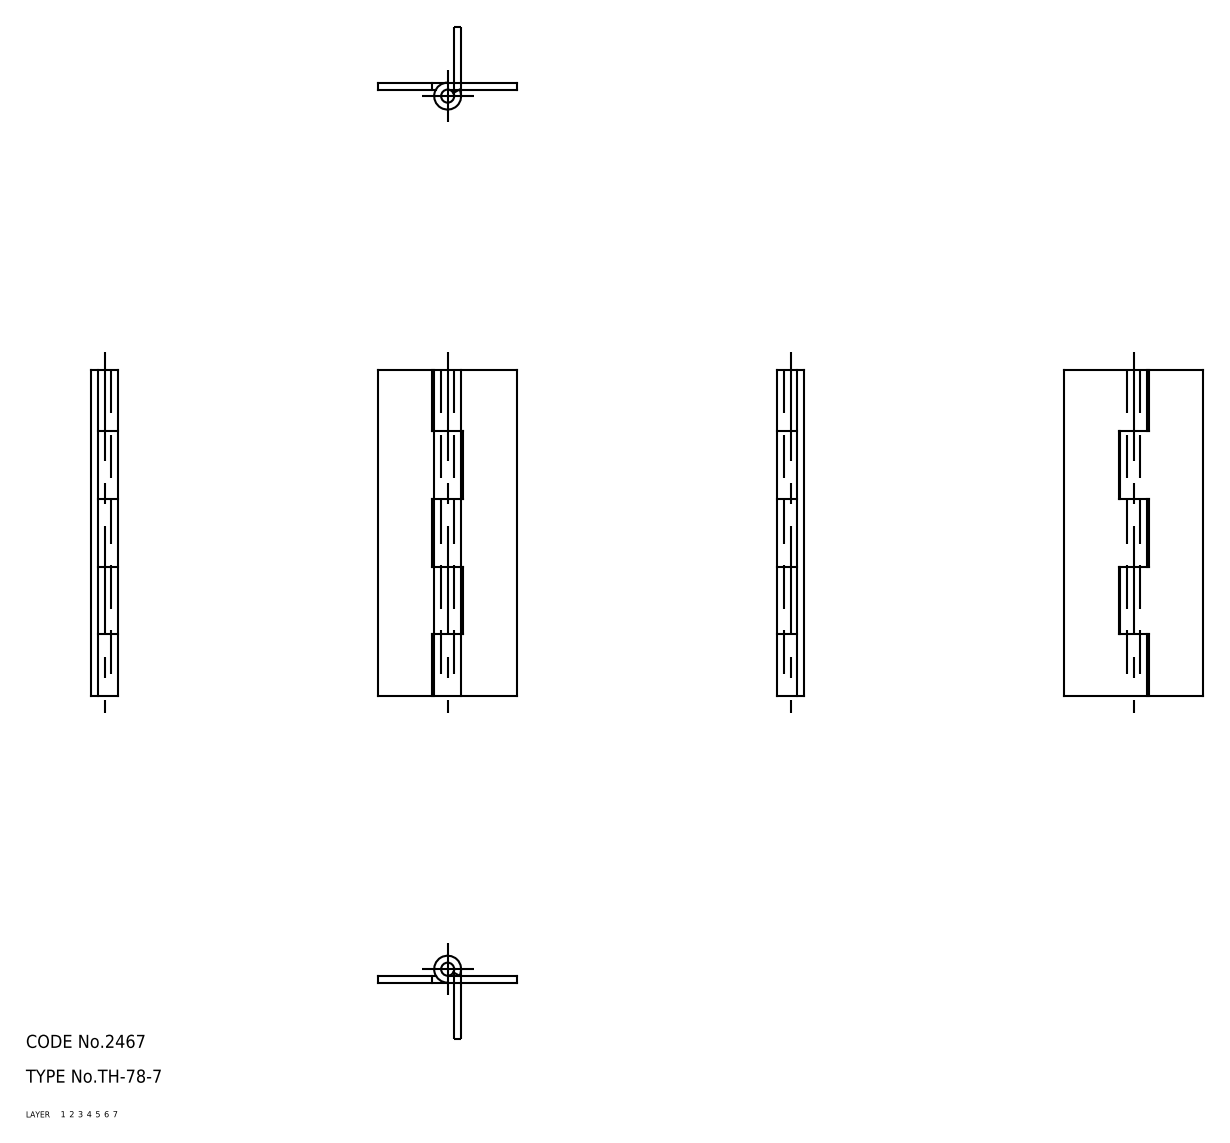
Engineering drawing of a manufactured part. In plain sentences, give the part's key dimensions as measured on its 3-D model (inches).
The part is named "hinge piece_B; hinge piece_A; shaft; TH_78_7_16873_36". Its 3-D file was written by "CADfix (AUTOMOTIVE_DESIGN)". It is 3 solids with 42 faces: 0 planar, 0 cylindrical and 42 other. Overall it measures 2.953 by 1.26 by 0.244 inches. Its volume is 0.329 cubic inches and its surface area 11.78 square inches.
